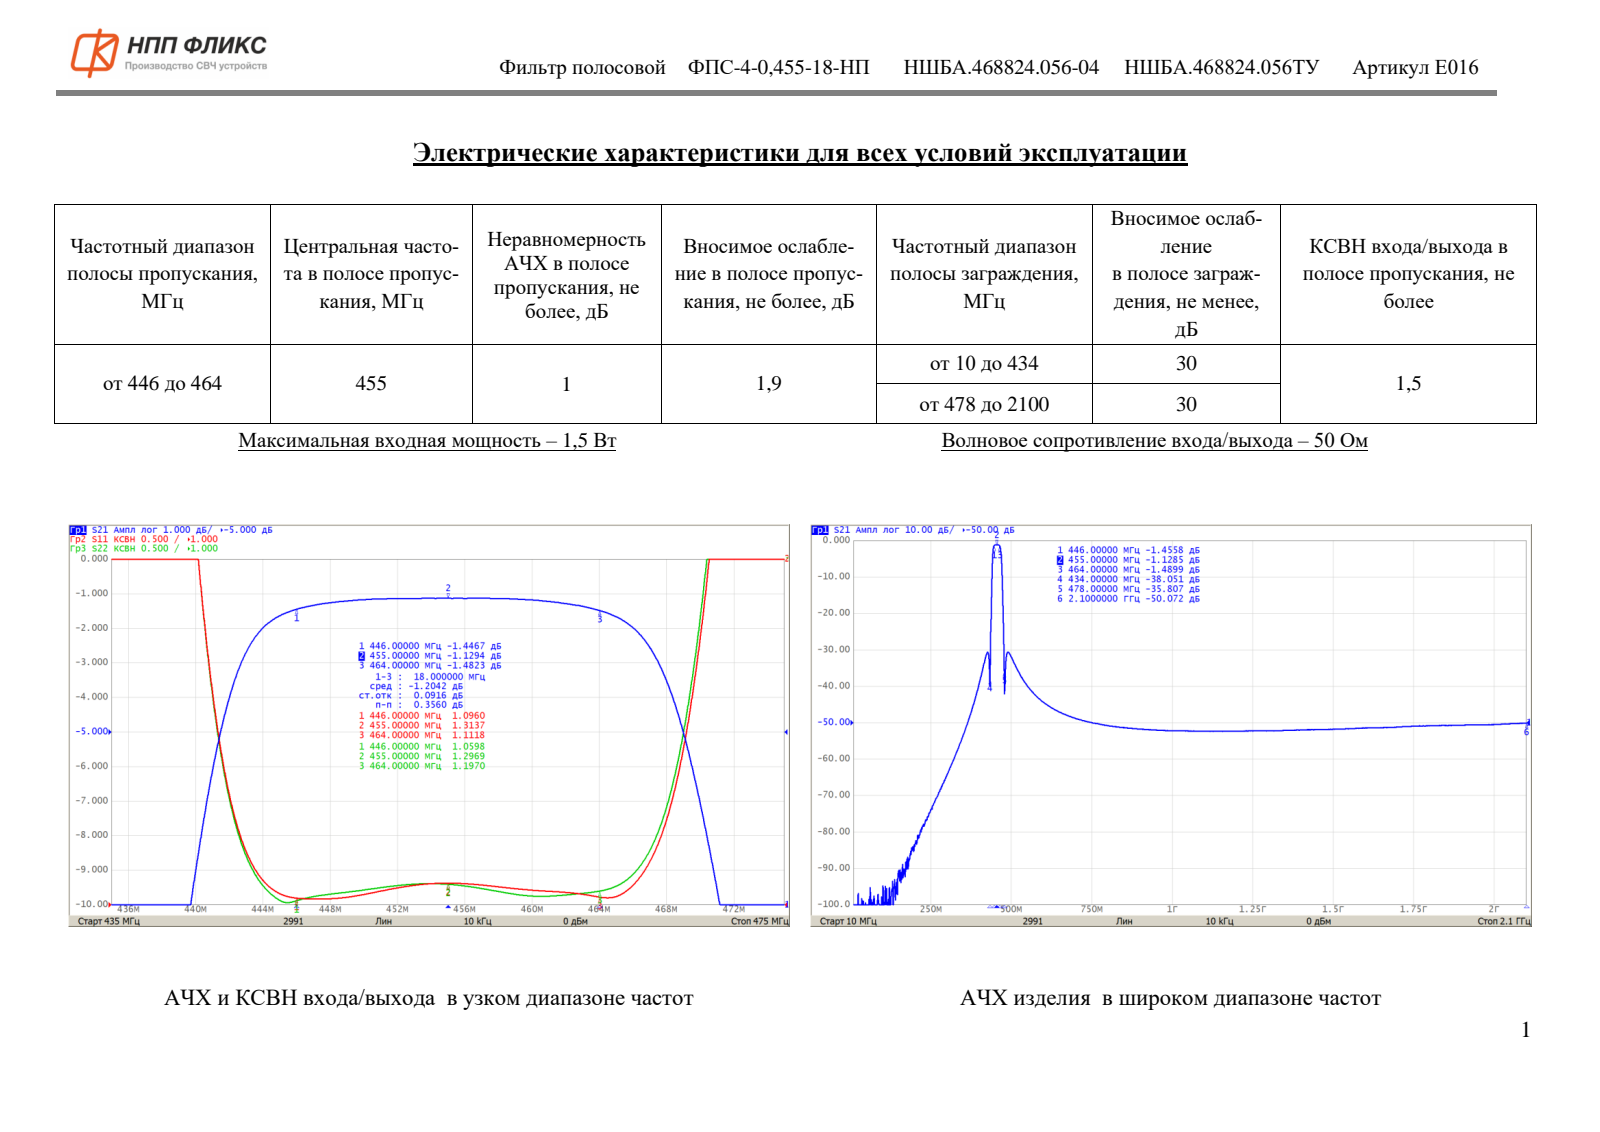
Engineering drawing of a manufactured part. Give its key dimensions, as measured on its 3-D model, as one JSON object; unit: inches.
{"part_name": "НШБА.468824.056-04_Фильтр ФПС-4-0,455-18-НП", "step_written_by": "ASCON Math Kernel (CONFIG_CONTROL_DESIGN)", "units": "inches", "bodies": {"solids": 1, "faces": 771, "planar": 570, "cylindrical": 89, "other": 112}, "overall_size": [1.181, 0.984, 0.666], "volume_in3": 0.078, "surface_area_in2": 9.506, "round_holes": [[0.031, 4], [0.02, 2]], "partial_cylinders_radius": [[0.02, 27], [0.012, 8], [0.018, 8], [0.024, 8], [0.039, 8], [0.01, 1], [0.03, 1], [0.035, 1]], "face_to_face_distances": [0.894, 0.032, 1.102, 0.666, 0.634, 0.654, 0.622, 0.882, 0.906, 1.091], "hole_center_spacings": [0.463, 1.049, 0.827, 0.894, 1.217, 1.071]}
